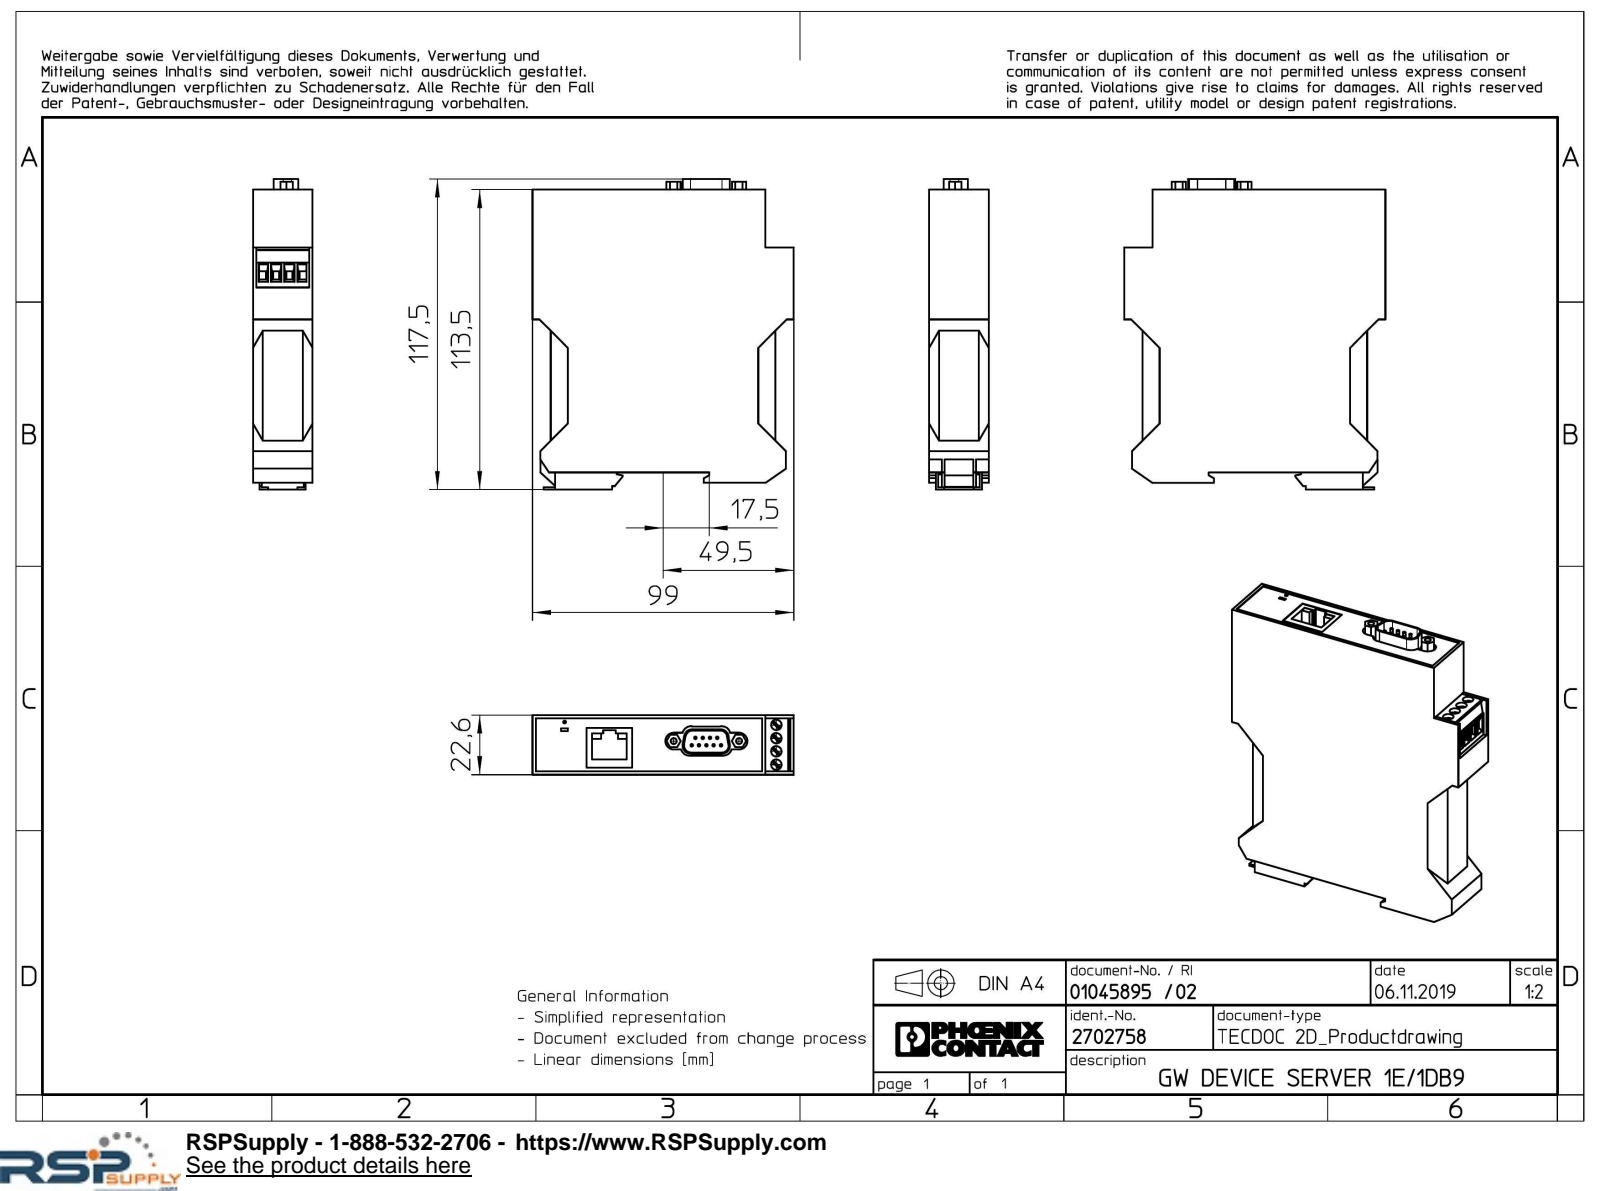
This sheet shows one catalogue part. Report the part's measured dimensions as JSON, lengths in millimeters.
{"part_name": "GW...1E_1DB9-select", "step_written_by": "Creo Elements/Direct Modeling 20.1A 29-Sep-2018 (C) Parametric Technology GmbH (AUTOMOTIVE_DESIGN)", "units": "millimeters", "bodies": {"solids": 1, "faces": 284, "planar": 238, "cylindrical": 46, "other": 0}, "overall_size": [117.5, 99, 22.6], "volume_mm3": 217974, "surface_area_mm2": 31622, "round_holes": [[4, 4], [2.29, 2], [1.08, 1]], "round_bosses_or_shafts": [[1, 9]], "partial_cylinders_radius": [[3.17, 6], [2.54, 4], [3.04, 4]], "face_to_face_distances": [22.6, 92.05, 4, 6.95, 106.8, 110.8, 85.1, 88.3, 81.35, 3.75], "hole_center_spacings": [5, 10, 14.18, 14.68, 15, 15.39, 16.72, 24.74]}
